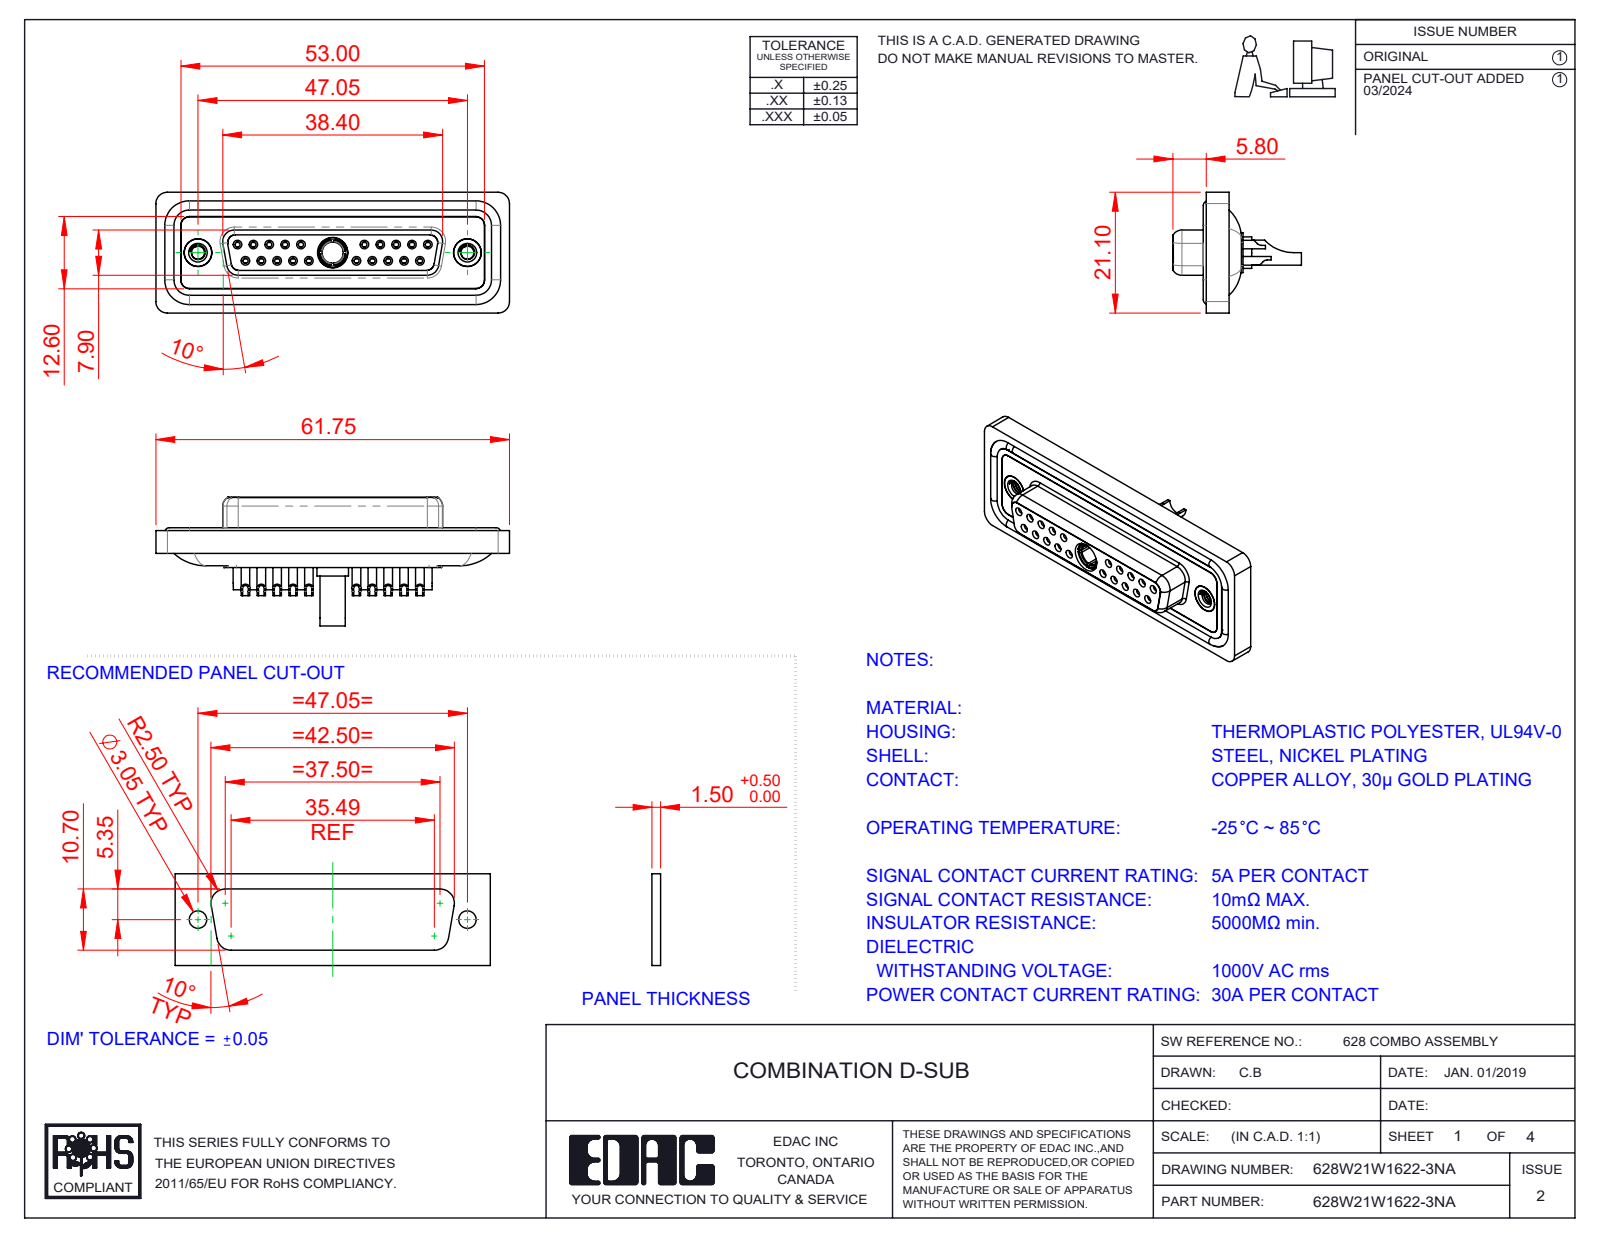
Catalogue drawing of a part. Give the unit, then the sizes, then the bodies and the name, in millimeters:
Units: millimetres
Overall size (bounding box): 61.75 × 22.45 × 21.1
Round holes (diameter × count): ⌀0.9 ×20, ⌀1 ×20, ⌀1.1 ×20, ⌀1.5 ×20, ⌀2 ×20, ⌀1.6 ×10, ⌀1.7 ×10, ⌀4.85 ×3, ⌀2.26 ×2, ⌀4 ×2, ⌀4.05 ×2, ⌀5 ×2
Round bosses / shafts (diameter × count): ⌀2.2 ×20, ⌀1.6 ×14, ⌀4.95 ×2, ⌀4.8 ×2, ⌀5.5 ×1, ⌀5.2 ×1, ⌀4.96 ×1, ⌀4.75 ×1
Partial cylindrical surfaces — rounded edges, fillets, slot ends (radius × count): R1.5 ×22, R2 ×18, R1.35 ×8, R1.6 ×8, R1 ×6, R0.25 ×4, R0.5 ×4, R0.6 ×4
Main face-to-face distances: 0.4, 1.8, 7.45, 5.65, 6.6, 0.5, 1.6, 7.05, 2.9, 1.1
Hole centre spacings: 3.16, 2.77, 5.54, 5.03, 8.31, 7.48, 16.62, 19.39
Volume: 8 440 mm³ · Surface area: 14 317 mm²
Bodies: 29 solids, 1564 faces (477 planar, 636 cylindrical, 451 other)
Part name (STEP PRODUCT): 628Combo Contact Row 2_22; 628Combo Threaded Rivet_A; 628Combo Shell Rear_25 Contacts; 628Combo Contact Row 1_22 (+5 more)
STEP written by: SolidWorks 2023 (CONFIG_CONTROL_DESIGN)
